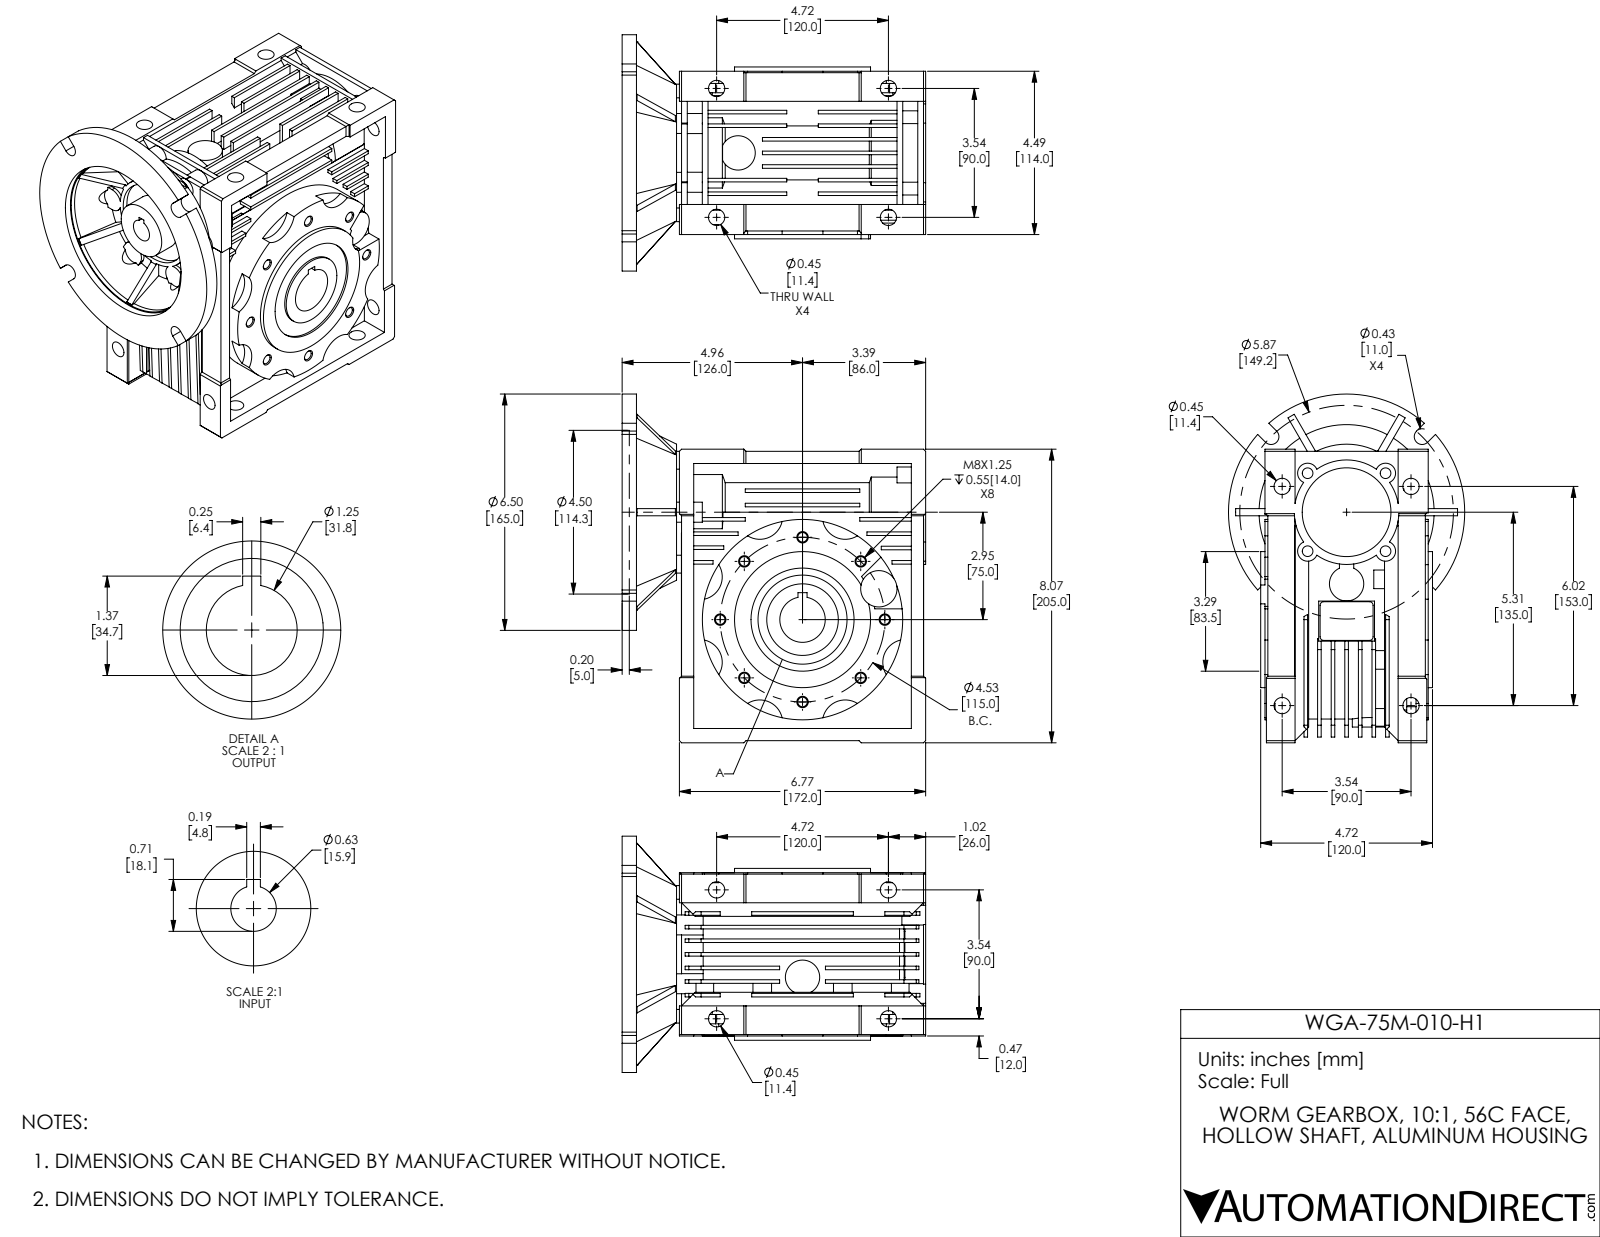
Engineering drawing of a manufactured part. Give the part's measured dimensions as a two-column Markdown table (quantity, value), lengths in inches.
| quantity | value |
| --- | --- |
| part name | WGA-75M-010-H1 |
| STEP written by | SolidWorks 2021 (CONFIG_CONTROL_DESIGN) |
| units | inches |
| bodies | 4 solids, 1179 faces (675 planar, 386 cylindrical, 118 other) |
| overall size | 9.587 × 8.346 × 6.496 |
| volume | 180.8 in³ |
| surface area | 779.6 in² |
| round holes (diameter × count) | 0.262 × 8, 0.448 × 8, 0.293 × 4, 0.625 × 1, 0.65 × 1, 1 × 1, 1.25 × 1, 1.535 × 1, 1.654 × 1, 1.969 × 1, 2.441 × 1, 2.677 × 1 |
| round bosses / shafts (diameter × count) | 0.512 × 14, 0.945 × 3, 6.496 × 1, 5.509 × 1, 5.465 × 1, 3.74 × 1, 2.992 × 1, 2.795 × 1 |
| partial cylindrical surfaces (radius × count) | 0.276 × 10, 0.63 × 8, 0.295 × 6, 0.335 × 6, 0.098 × 4, 0.217 × 4, 1.299 × 1, 1.417 × 1 |
| main face-to-face distances | 0.374, 0.098, 0.472, 0.748, 0.276, 1.122, 1.496, 0.394, 0.65, 0.846 |
| hole center spacings | 2.264, 1.733, 3.202, 4.183, 1.515, 2.143, 3.543, 4.528 |
